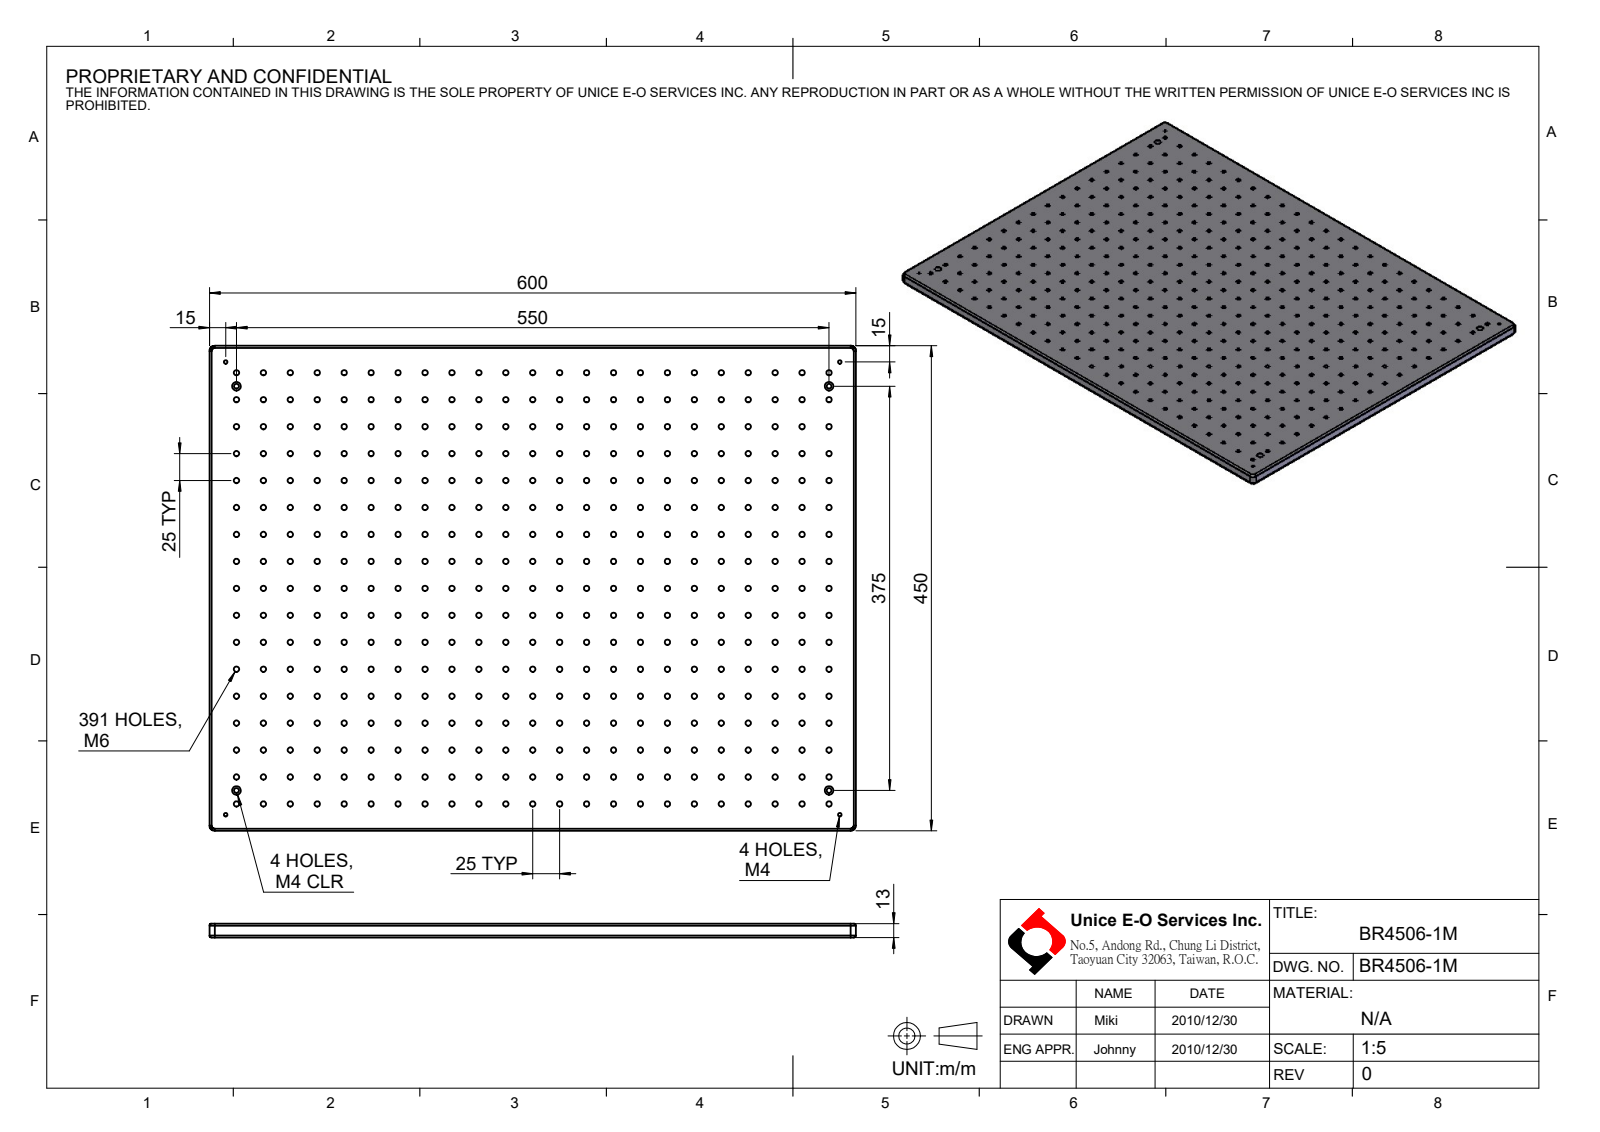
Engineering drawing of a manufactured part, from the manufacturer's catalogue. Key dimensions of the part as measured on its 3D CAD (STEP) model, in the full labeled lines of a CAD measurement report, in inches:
Part name (STEP PRODUCT): BR4506-1M
STEP written by: SolidWorks 2016 (CONFIG_CONTROL_DESIGN)
Units: inches
Bodies: 1 solid, 836 faces (10 planar, 818 cylindrical, 8 other)
Overall size (bounding box): 23.622 × 17.717 × 0.512
Volume: 207.7 in³ · Surface area: 975.5 in²
Round holes (diameter × count): ⌀0.197 ×391, ⌀0.13 ×4, ⌀0.177 ×4, ⌀0.315 ×4
Partial cylindrical surfaces — rounded edges, fillets, slot ends (radius × count): R0.079 ×8, R0.197 ×4
Main face-to-face distances: 0.512, 17.717, 23.622, 0.276, 0.236
Hole centre spacings: 0.984, 1.969, 2.953, 4.921, 3.937, 5.906, 6.89, 7.874
